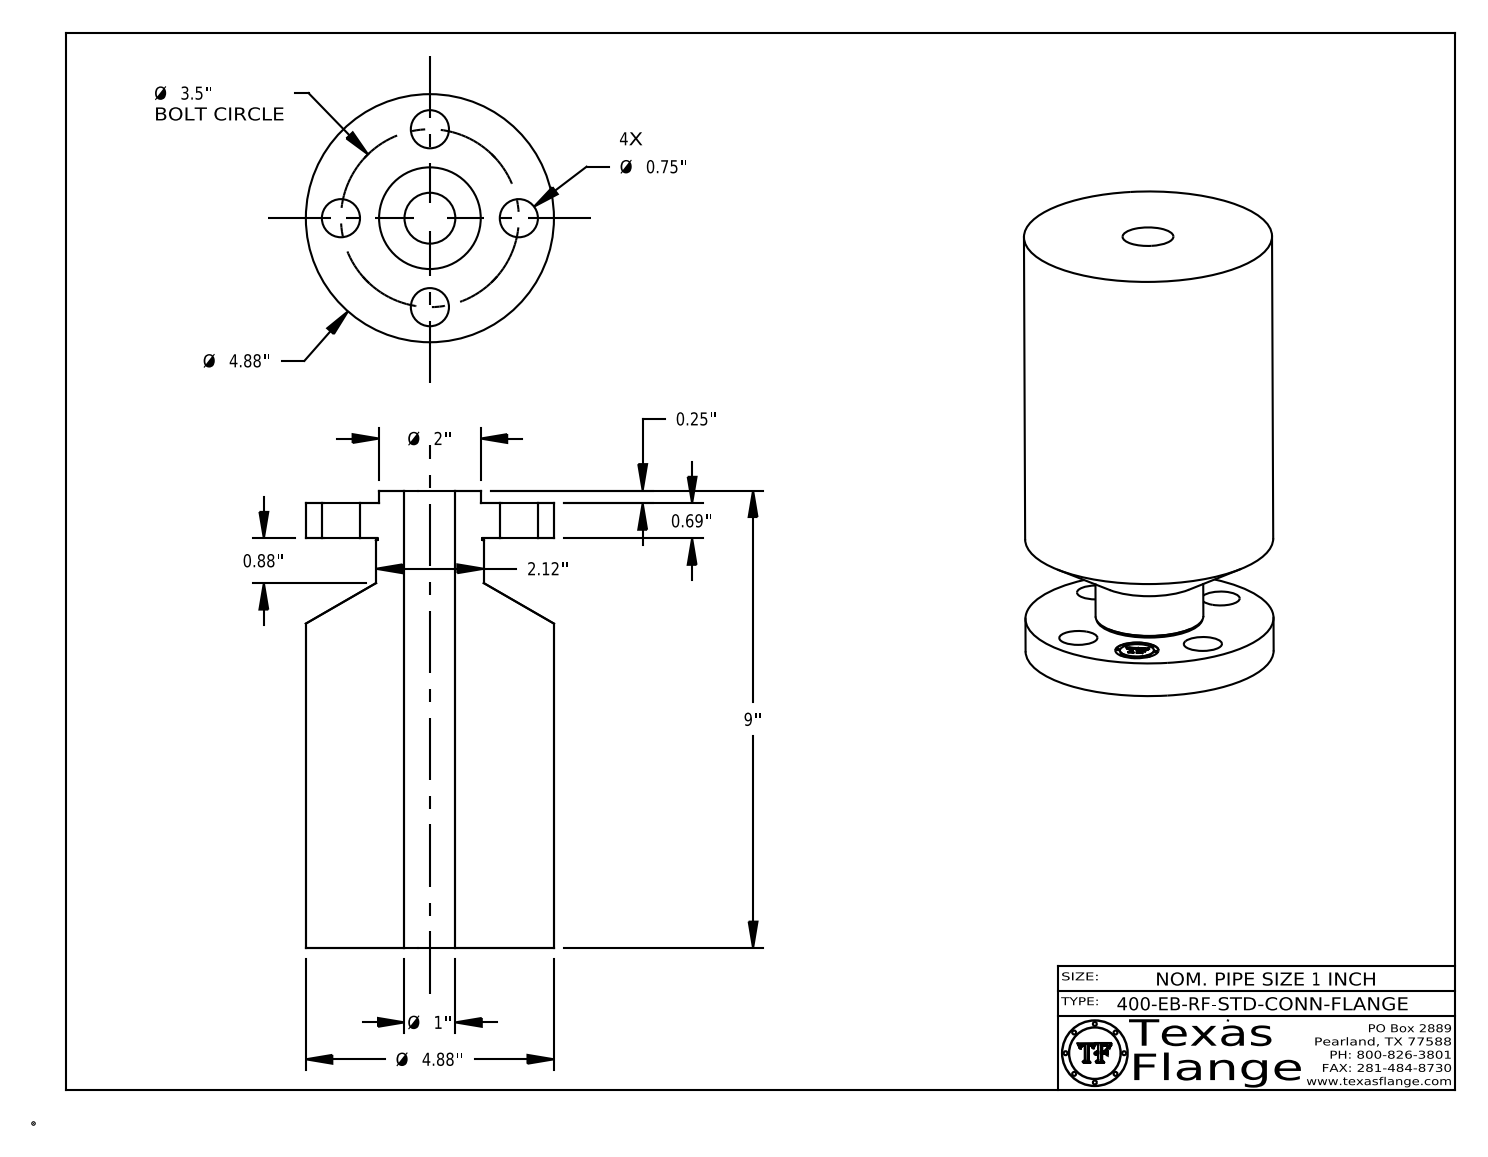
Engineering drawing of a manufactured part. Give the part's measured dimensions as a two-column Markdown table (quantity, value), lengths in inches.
| quantity | value |
| --- | --- |
| part name | 1-400-EB-RF-STD-CONN-FLANGE |
| STEP written by | CATIA V5 STEP AP214 (AUTOMOTIVE_DESIGN) |
| units | inches |
| bodies | 1 solid, 413 faces (369 planar, 38 cylindrical, 6 other) |
| overall size | 9 × 4.88 × 4.88 |
| volume | 136 in³ |
| surface area | 216 in² |
| round holes (diameter × count) | 0.75 × 4, 0.85 × 1, 1 × 1 |
| round bosses / shafts (diameter × count) | 0.051 × 8, 4.88 × 1, 2.12 × 1, 2 × 1, 0.67 × 1 |
| main face-to-face distances | 8.75, 0.69, 8.06, 0.25, 0.94, 9, 0.935, 0.685, 8.065, 0.016 |
| hole center spacings | 1.75, 2.475, 1.339, 3.233, 3.5 |
